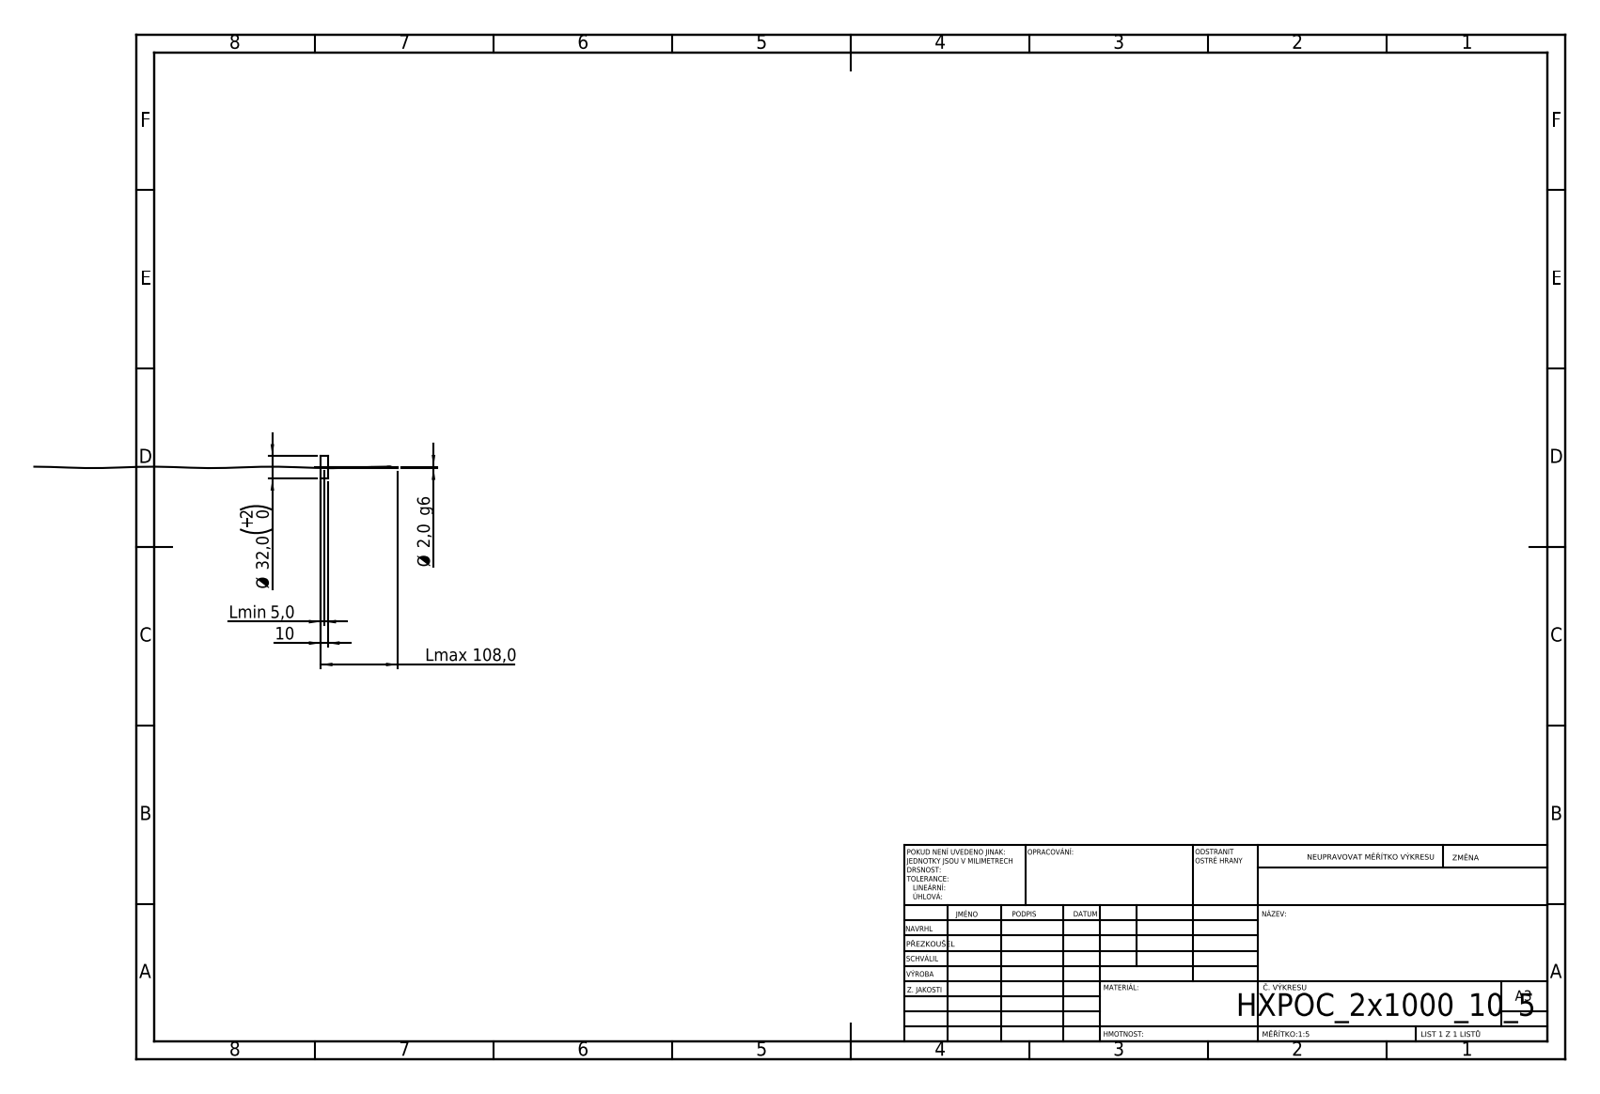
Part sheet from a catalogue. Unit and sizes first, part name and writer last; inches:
Units: inches
Overall size (bounding box): 4.252 × 1.26 × 1.26
Round bosses / shafts (diameter × count): ⌀1.26 ×1, ⌀0.079 ×1
Main face-to-face distances: 0.394, 4.252, 3.858, 3.85, 3.457, 0.402
Volume: 0.509 in³ · Surface area: 5.028 in²
Bodies: 1 solid, 11 faces (4 planar, 5 cylindrical, 2 other)
STEP written by: SolidWorks 2019 (CONFIG_CONTROL_DESIGN)
